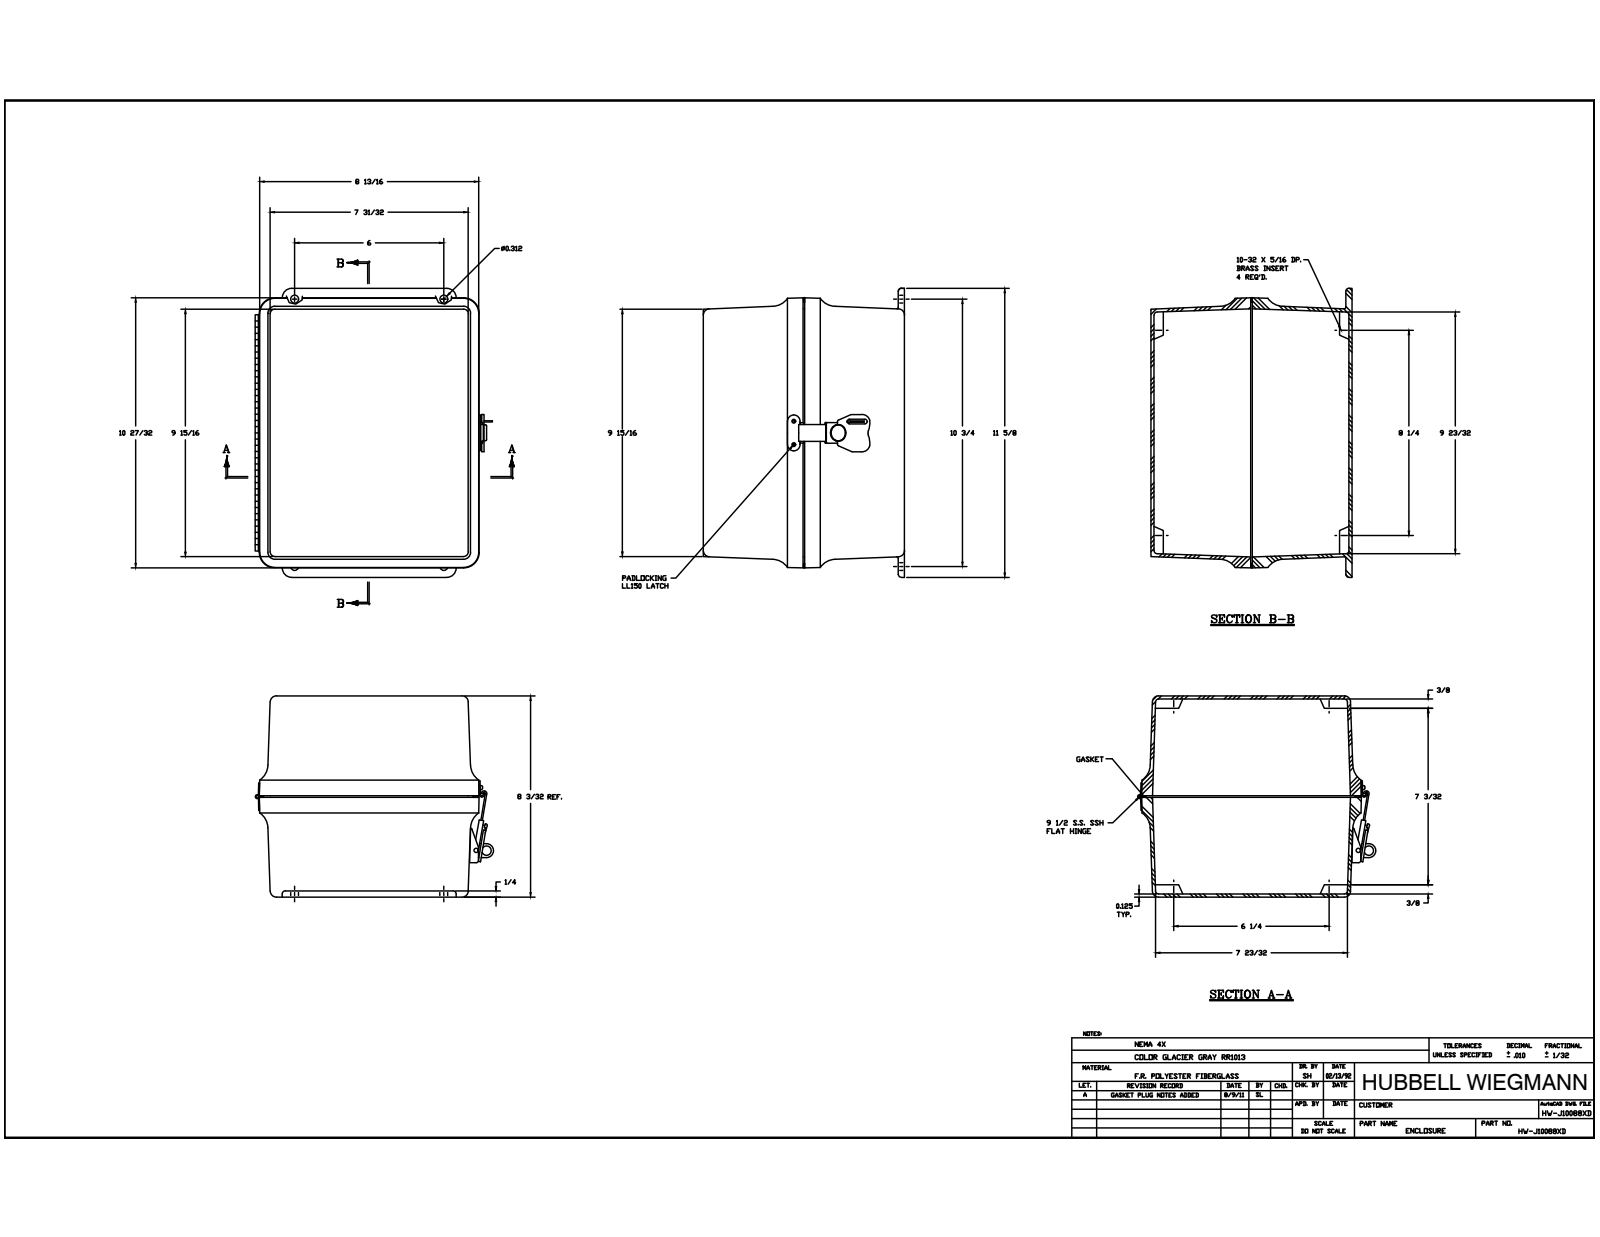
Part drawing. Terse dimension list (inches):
name: J1008SSH; RMINS45821P_105; RMINS45821P_106; RMINS45821P_107 (+8 more)
written by: Autodesk Inventor 2014 (AUTOMOTIVE_DESIGN)
unit: in
bodies: 37 solids, 1189 faces (431 planar, 456 cylindrical, 302 other)
size: 11.625 × 9.552 × 8.088
volume: 79.51 in³; area: 1 006 in²
holes: 12× ⌀0.14, 11× ⌀0.152, 8× ⌀0.136, 6× ⌀0.156, 4× ⌀0.218, 2× ⌀0.13, 2× ⌀0.165, 2× ⌀0.197, 1× ⌀0.085, 1× ⌀0.106, 1× ⌀0.118, 1× ⌀0.138
bosses: 12× ⌀0.25, 12× ⌀0.125, 6× ⌀0.27, 1× ⌀0.583, 1× ⌀0.524, 1× ⌀0.209, 1× ⌀0.185, 1× ⌀0.155
rounds: 88× R0.031, 13× R0.75, 12× R0.125, 12× R0.25, 10× R0.079, 4× R0.039, 4× R0.047, 4× R0.086
face distances: 0.125, 7.838, 7.958, 8.088, 0.125, 7.963, 7.963, 9.97, 8.233, 10.244
hole spacings: 2.5, 6, 1.337, 7.251, 9.25, 10.35, 11.677, 0.681
